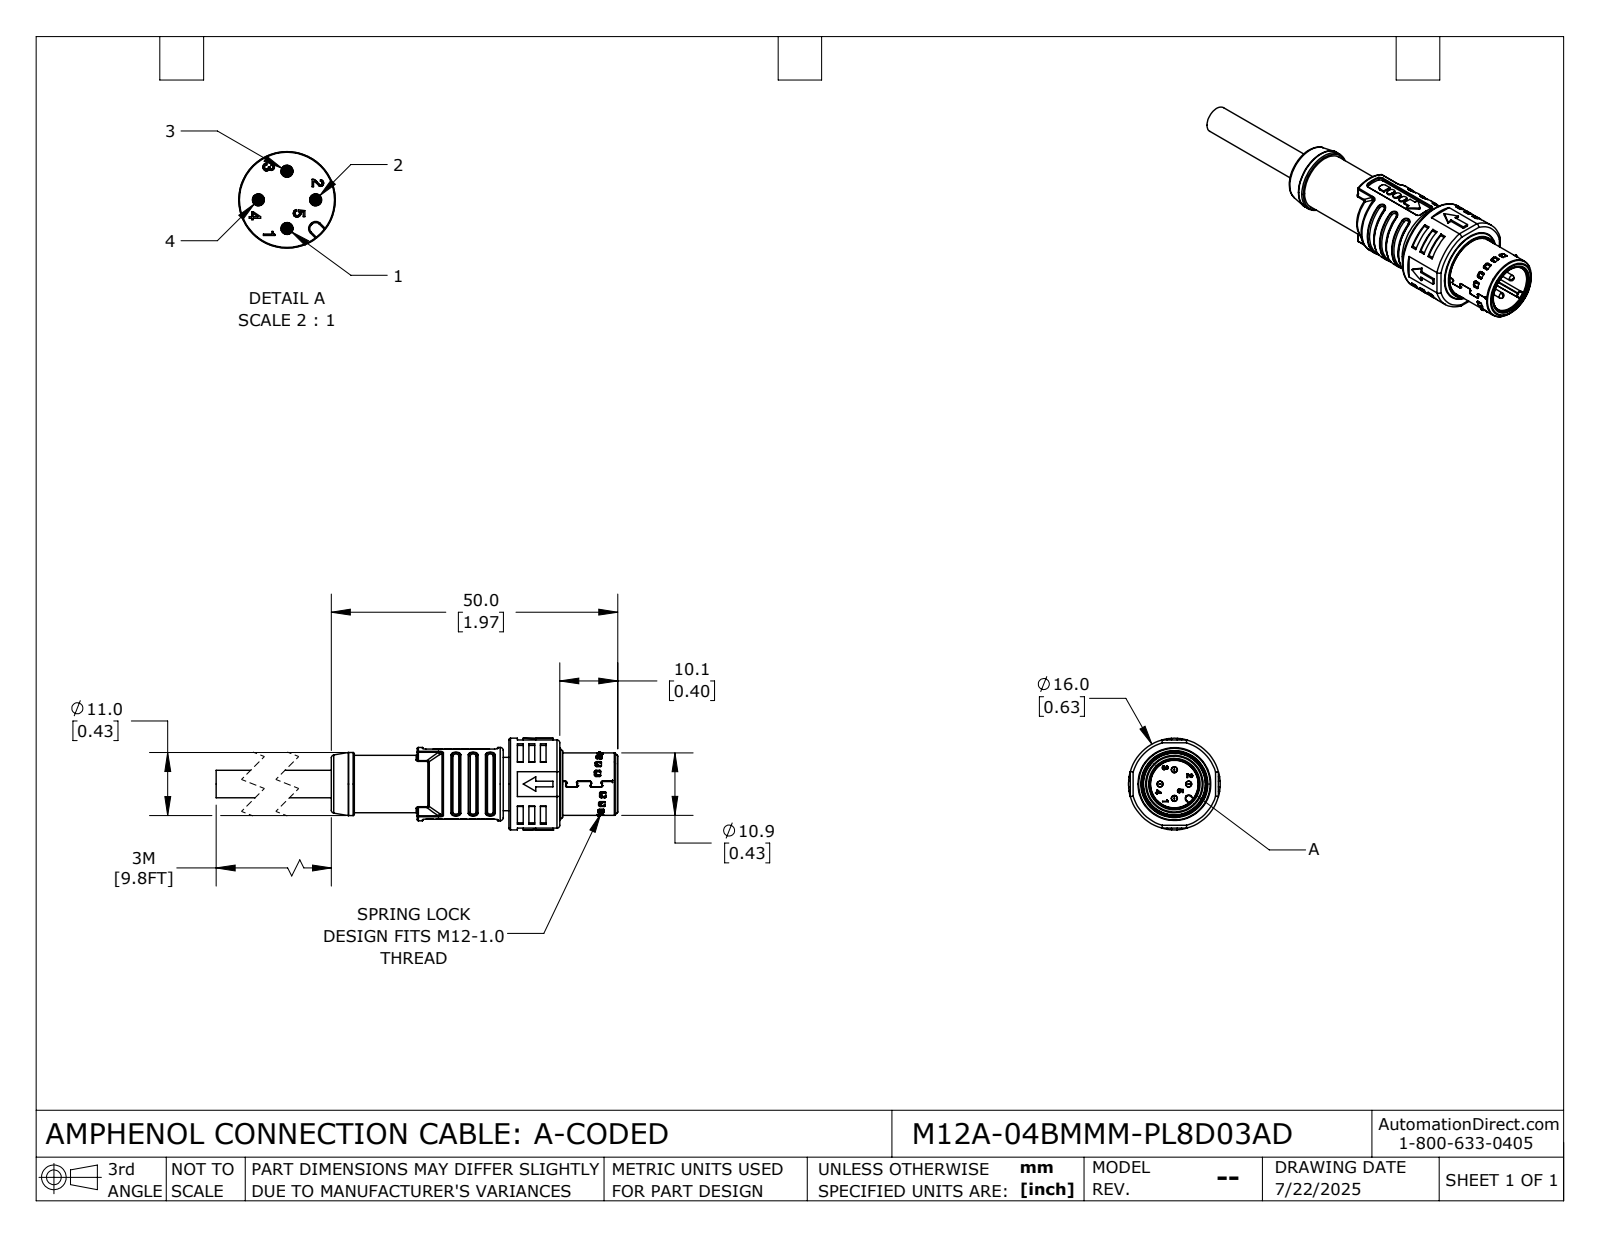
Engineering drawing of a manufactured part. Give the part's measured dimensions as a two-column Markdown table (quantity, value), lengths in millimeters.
| quantity | value |
| --- | --- |
| part name | M12A-04BMMM-PL8D03AD |
| STEP written by | SolidWorks 2024 (CONFIG_CONTROL_DESIGN) |
| units | millimeters |
| bodies | 1 solid, 2276 faces (1081 planar, 672 cylindrical, 523 other) |
| overall size | 72.7 × 16 × 16 |
| volume | 5 180 mm³ |
| surface area | 5 970 mm² |
| round holes (diameter × count) | 1 × 4, 1.4 × 4, 8.3 × 1, 9 × 1, 10.2 × 1, 10.5 × 1, 11.5 × 1, 11.8 × 1, 14.2 × 1 |
| round bosses / shafts (diameter × count) | 1.4 × 4, 1 × 4, 16 × 1, 14.1 × 1, 12.8 × 1, 12.4 × 1, 11 × 1, 10.9 × 1 |
| partial cylindrical surfaces (radius × count) | 0.2 × 114, 0.3 × 66, 0.3 × 64, 0.2 × 44, 0.5 × 38, 0.1 × 12, 0.7 × 11, 0.1 × 10 |
| main face-to-face distances | 1, 10.1, 8.9, 8.6, 2.5, 1.5, 1.2, 32.5, 15.4, 41.1 |
| hole center spacings | 2.5, 3.5, 5 |
